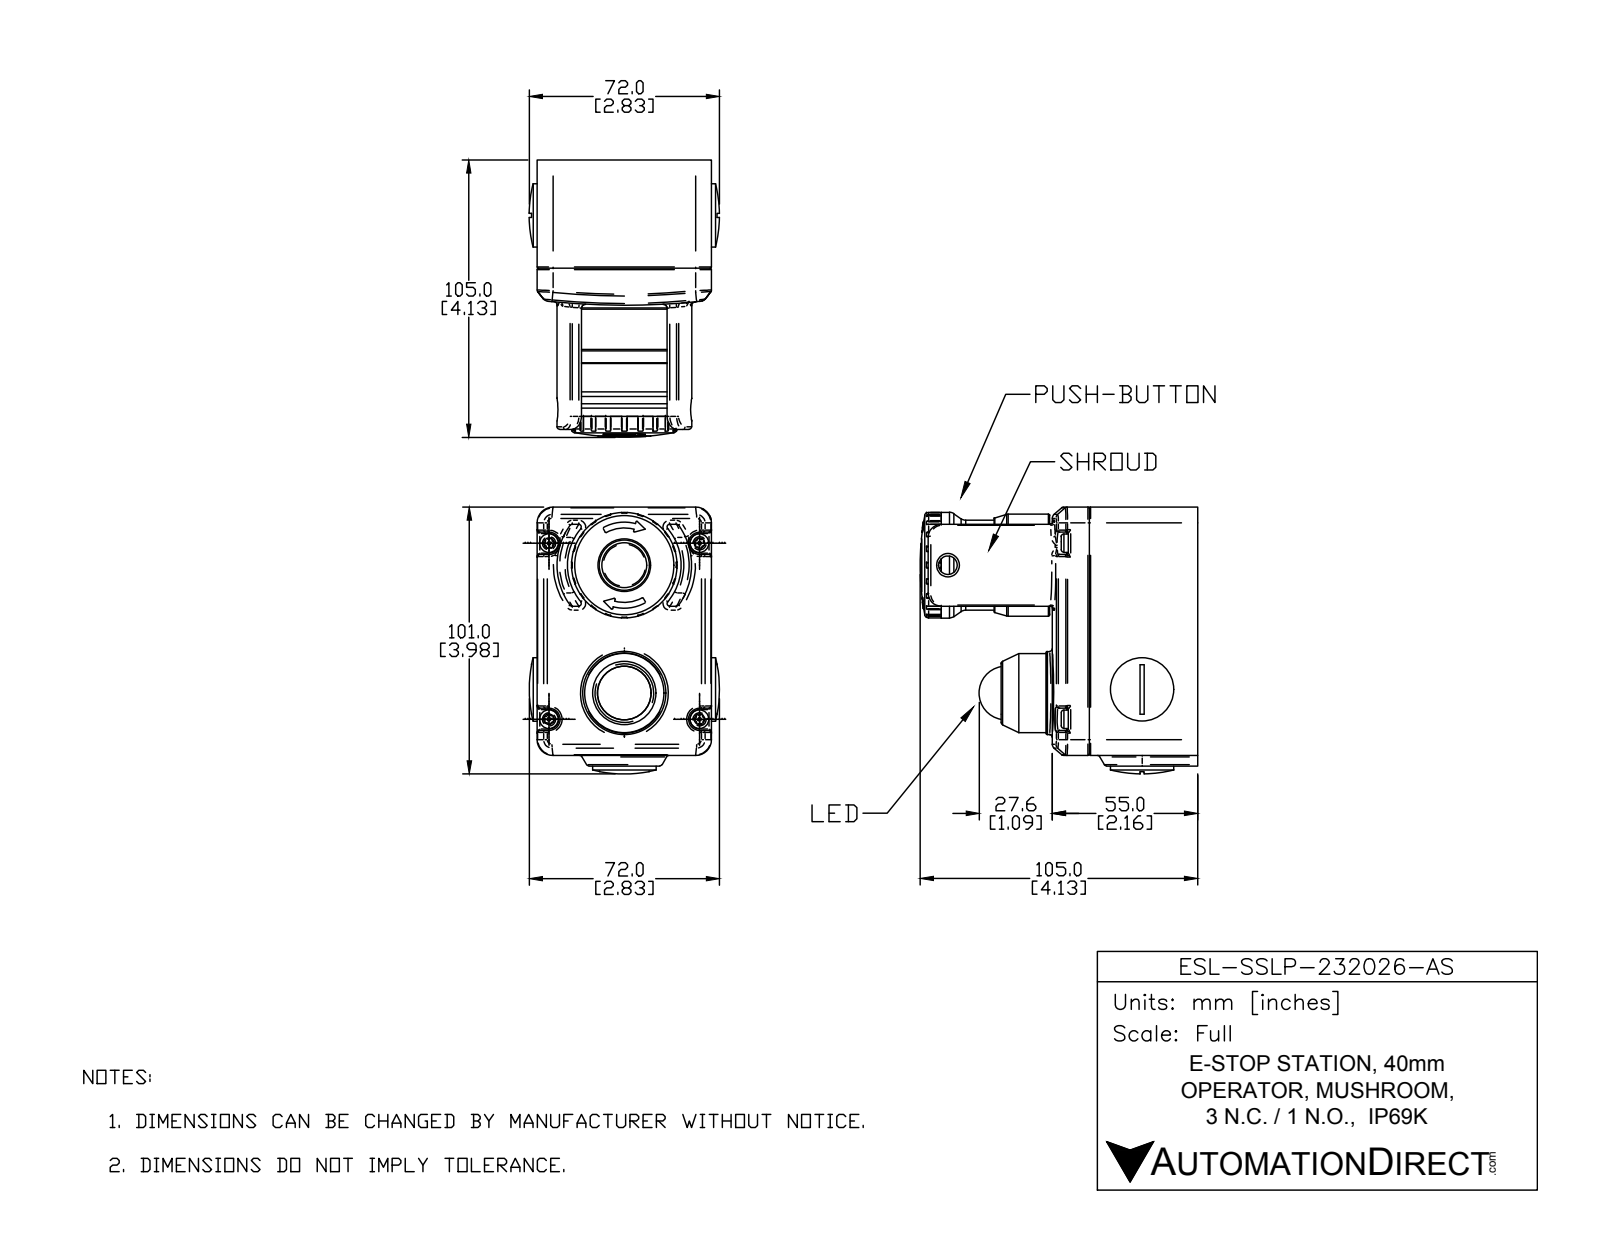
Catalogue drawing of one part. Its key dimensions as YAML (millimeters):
part_name: "ESL-SSLP-232026-AS"
step_written_by: "SolidWorks 2016 (AUTOMOTIVE_DESIGN)"
units: millimeters
bodies: {solids: 13, faces: 797, planar: 227, cylindrical: 287, other: 283}
overall_size: [105, 100.99, 71.98]
volume: 382565
surface_area: 72756
round_holes:
  - {diameter: 4.5, count: 4}
  - {diameter: 7, count: 1}
  - {diameter: 28.04, count: 1}
  - {diameter: 31.1, count: 1}
  - {diameter: 37, count: 1}
round_bosses_or_shafts:
  - {diameter: 7, count: 4}
  - {diameter: 1, count: 4}
  - {diameter: 24, count: 2}
  - {diameter: 40, count: 1}
  - {diameter: 38.6, count: 1}
  - {diameter: 34, count: 1}
  - {diameter: 31.4, count: 1}
  - {diameter: 30, count: 1}
partial_cylinders:
  - {radius: 0.1, count: 80}
  - {radius: 0.76, count: 24}
  - {radius: 0.5, count: 14}
  - {radius: 1, count: 13}
  - {radius: 1.5, count: 6}
  - {radius: 0.2, count: 4}
  - {radius: 4.2, count: 4}
  - {radius: 6, count: 4}
face_to_face_distances: [41, 66, 56, 15, 98, 4, 94, 56.8, 15.8, 0.8]
hole_center_spacings: [31.38, 32.23, 54, 69.83, 71.31, 82, 98.18, 48.4]
